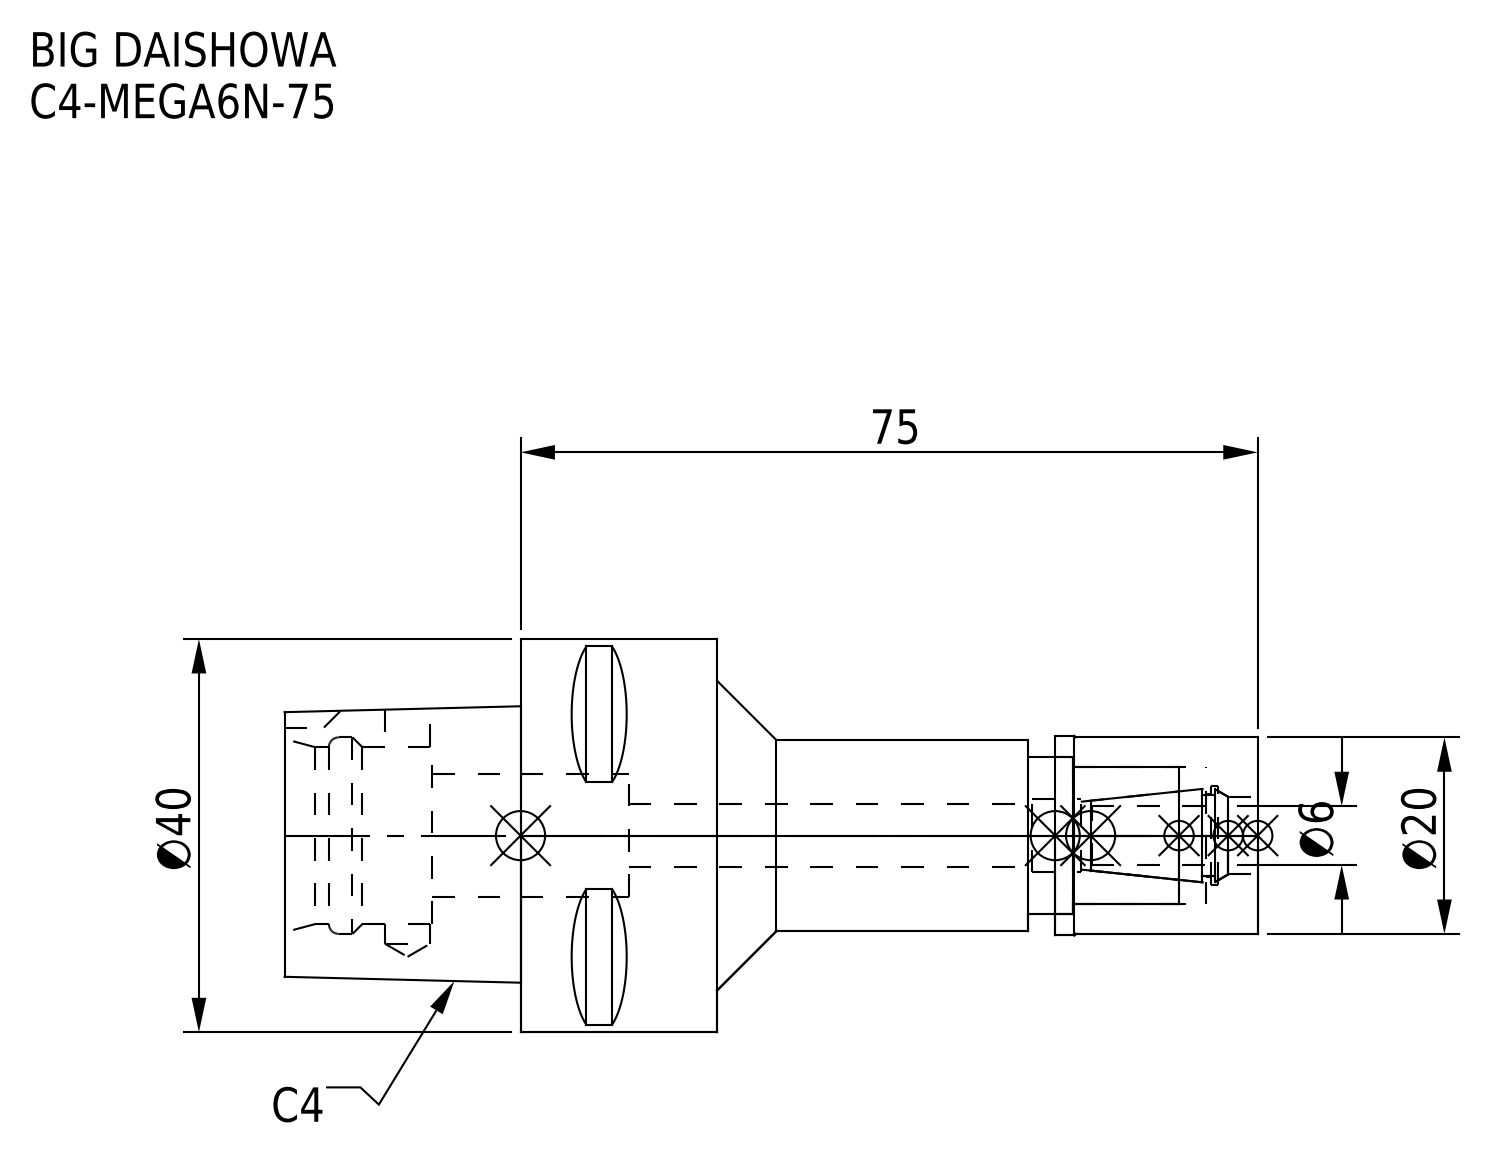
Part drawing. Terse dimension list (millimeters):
name: C4-MEGA6N-75-060.stp; C4-MEGA6N-75-060-FreeParts; C4-MEGA6N-75-060_ASM.stp; C4-MEGA6N-75_3.stp (+3 more)
written by: SolidWorks 2019 (CONFIG_CONTROL_DESIGN)
unit: mm
bodies: 2 solids, 95 faces (38 planar, 39 cylindrical, 18 other)
size: 99 × 40 × 40
volume: 47 179 mm³; area: 15 188 mm²
holes: 1× ⌀4.6, 1× ⌀6.4, 1× ⌀7.5, 1× ⌀7.9, 1× ⌀8.5, 1× ⌀10, 1× ⌀12.5, 1× ⌀14, 1× ⌀16, 1× ⌀18, 1× ⌀20
bosses: 1× ⌀40, 1× ⌀20.3, 1× ⌀19.5
rounds: 1× R3
face distances: 20, 55, 75, 9, 99, 44, 24, 15, 84, 29
